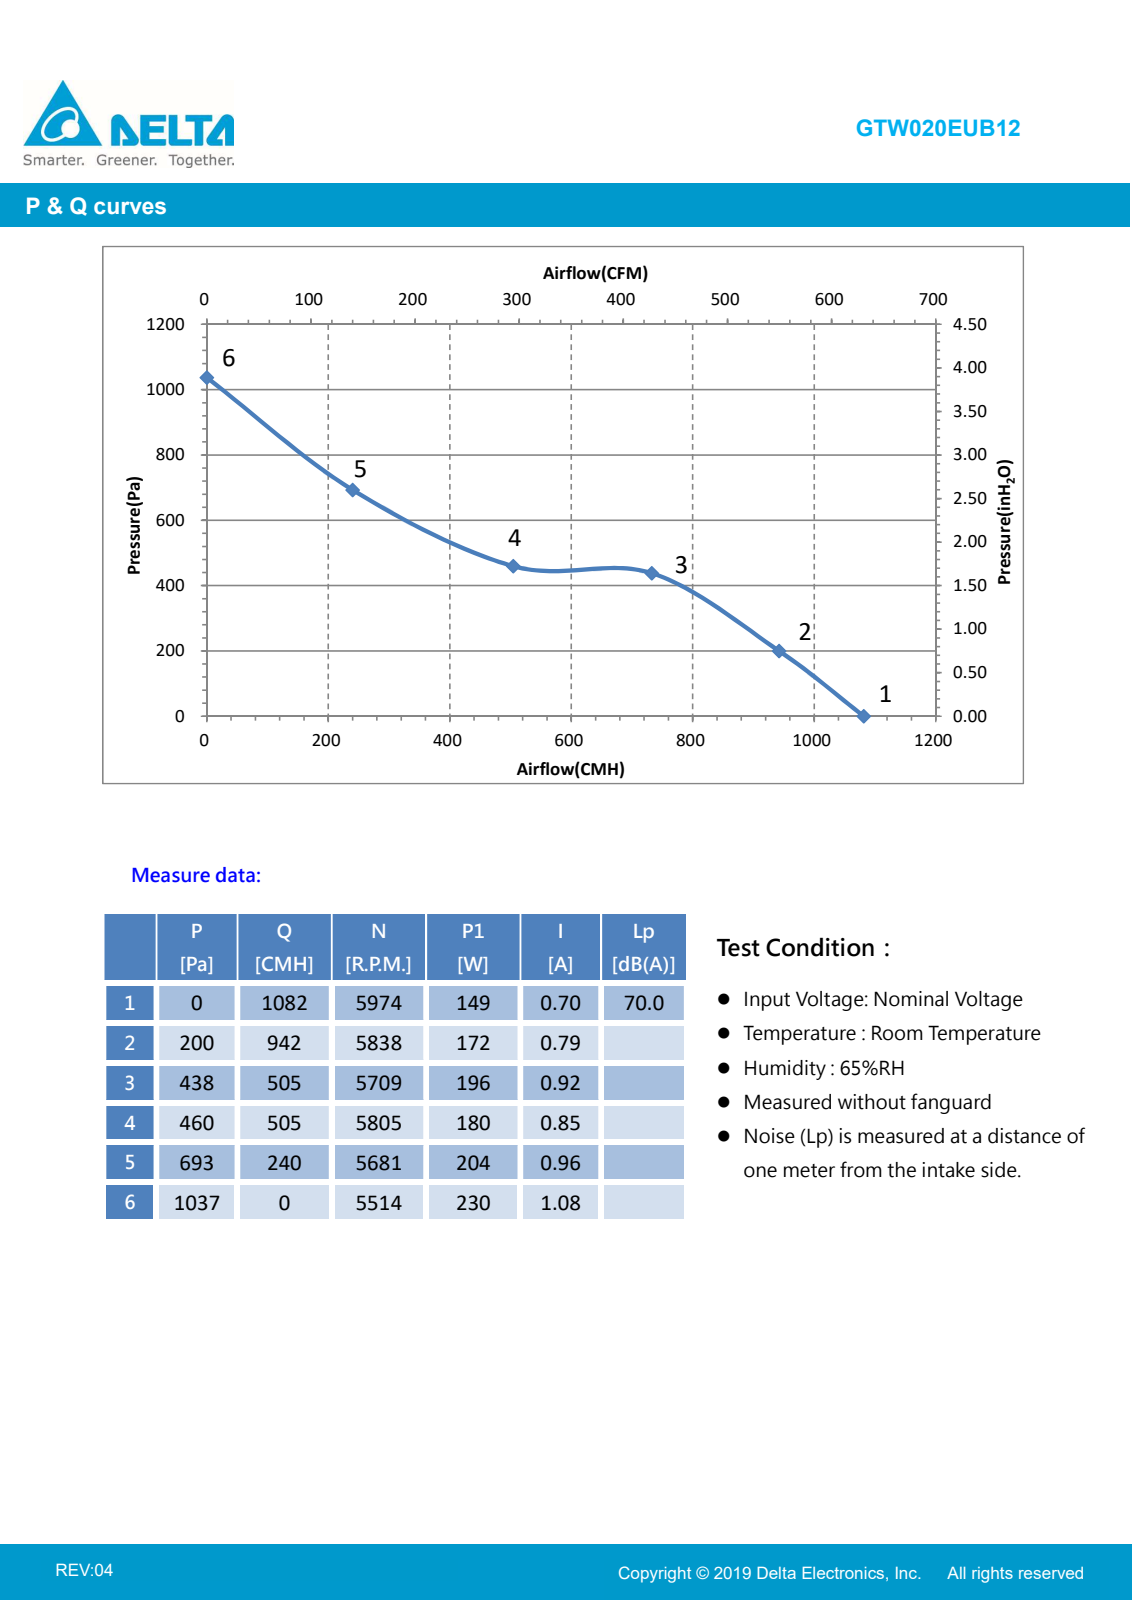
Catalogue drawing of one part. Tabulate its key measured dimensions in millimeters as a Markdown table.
| quantity | value |
| --- | --- |
| part name | GTW017EUB12-3D; 410130950001a-1; GUARD-INLET-1; 3105128100-M4-1 (+8 more) |
| STEP written by | SolidWorks 2011 (AUTOMOTIVE_DESIGN) |
| units | millimeters |
| bodies | 35 solids, 1173 faces (323 planar, 381 cylindrical, 469 other) |
| overall size | 217.06 × 217.06 × 126.42 |
| volume | 1 228 000 mm³ |
| surface area | 262 332 mm² |
| round holes (diameter × count) | 3 × 4, 4 × 4, 4.5 × 4, 7 × 3, 5 × 2, 7.7 × 2, 8.5 × 2, 10 × 1, 91.81 × 1 |
| round bosses / shafts (diameter × count) | 1.6 × 24, 8 × 4, 4 × 4, 2.5 × 4, 12.5 × 2, 11.5 × 2, 9.8 × 2, 200 × 1 |
| partial cylindrical surfaces (radius × count) | 1 × 46, 0.5 × 21, 2 × 12, 6 × 6, 4.65 × 4, 5.91 × 4, 7.88 × 4, 9.14 × 4 |
| main face-to-face distances | 18.5, 18.6, 21, 20.9, 2.4, 53.1, 74, 53, 71.6, 8 |
| hole center spacings | 104.02, 147.1, 16, 52, 15.99, 58.42, 208.03, 15.98 |
